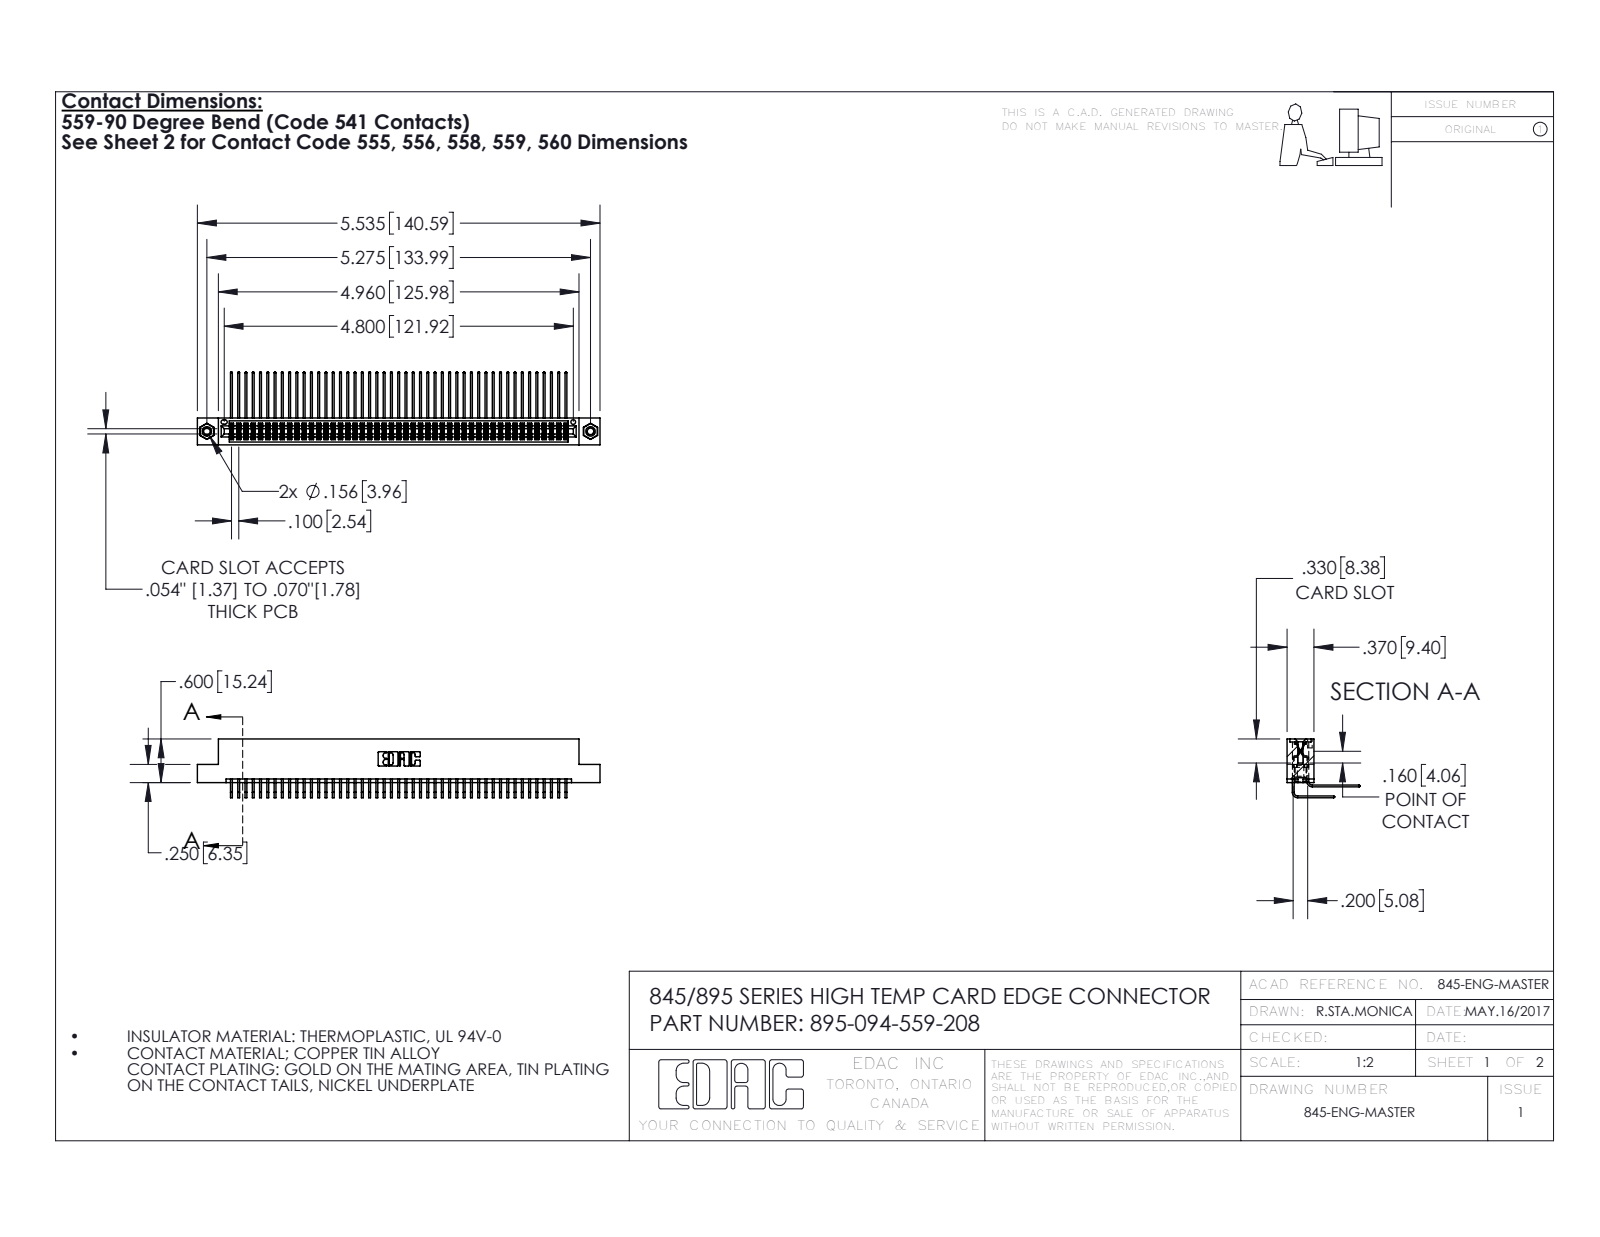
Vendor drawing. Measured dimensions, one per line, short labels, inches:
name: 345 Part_Flush Mounting Lugs - 0.156 Dia-TI; 395-094-559-208; 345-292-001_558 559 Tail - 1; 345-250-001_345-250-003-102 (+1 more)
written by: SolidWorks 2016 (CONFIG_CONTROL_DESIGN)
unit: in
bodies: 97 solids, 5074 faces (3402 planar, 1656 cylindrical, 16 other)
size: 5.535 × 1.005 × 0.809
volume: 0.869 in³; area: 36.75 in²
holes: 2× ⌀0.089, 2× ⌀0.125, 2× ⌀0.156, 1× ⌀0.064
bosses: 2× ⌀0.155
rounds: 142× R0.006, 22× R0.01, 6× R0.007, 6× R0.031, 3× R0.026, 2× R0.014, 2× R0.019, 2× R0.022
face distances: 0.072, 0.298, 0.2, 0.37, 0.098, 0.272, 0.025, 0.225, 0.175, 0.15
hole spacings: 0.27, 5.039, 5.275
